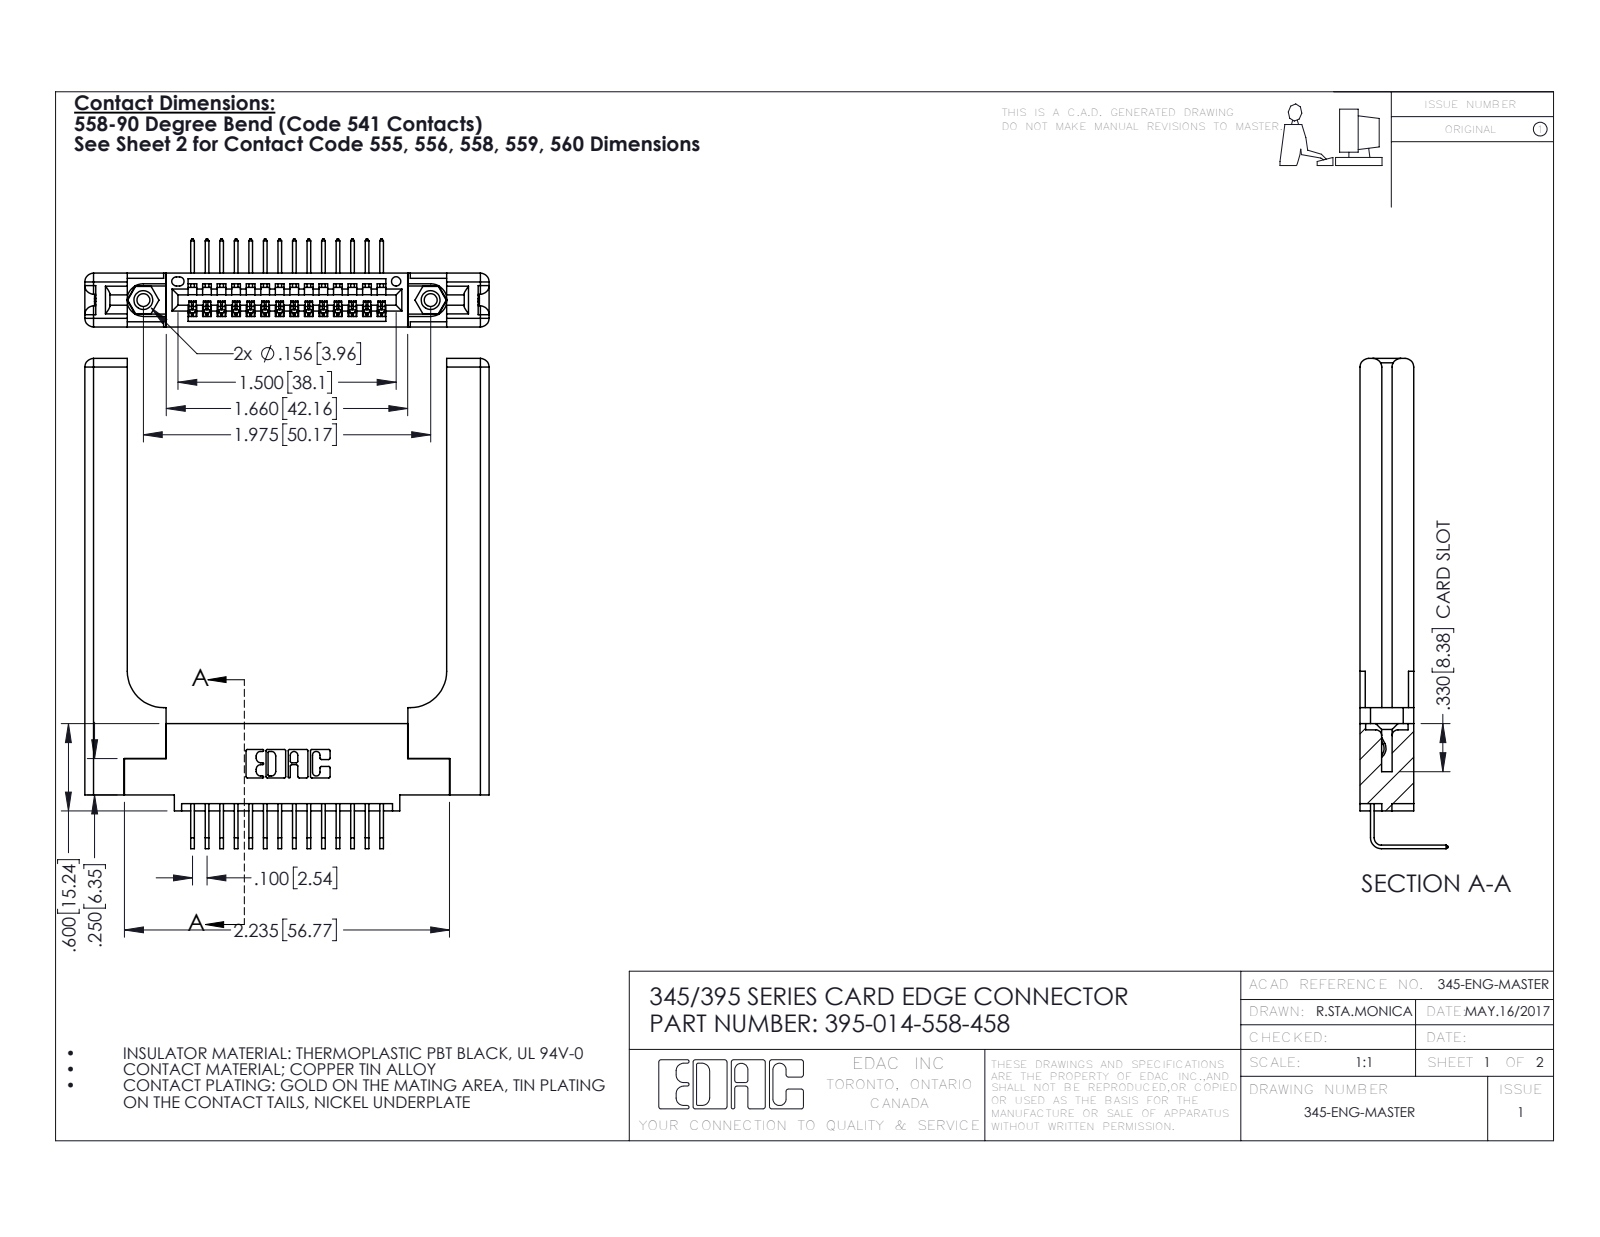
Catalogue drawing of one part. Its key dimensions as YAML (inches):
part_name: "345-292-001_558 Tail - 2; 345 Part_0.110 Offset - 0.156 Dia-TH; 395-014-558-458; 345-220-058_345-220-058 (+1 more)"
step_written_by: "SolidWorks 2016 (CONFIG_CONTROL_DESIGN)"
units: inches
bodies: {solids: 19, faces: 1226, planar: 820, cylindrical: 346, other: 60}
overall_size: [3.369, 2.779, 0.605]
volume: 0.913
surface_area: 21.47
round_holes:
  - {diameter: 0.089, count: 2}
  - {diameter: 0.125, count: 2}
  - {diameter: 0.156, count: 2}
  - {diameter: 0.064, count: 1}
round_bosses_or_shafts:
  - {diameter: 0.155, count: 2}
partial_cylinders:
  - {radius: 0.006, count: 28}
  - {radius: 0.01, count: 22}
  - {radius: 0.06, count: 16}
  - {radius: 0.007, count: 6}
  - {radius: 0.031, count: 6}
  - {radius: 0.026, count: 3}
  - {radius: 0.03, count: 2}
  - {radius: 0.031, count: 2}
face_to_face_distances: [0.37, 0.072, 0.298, 0.15, 0.148, 0.077, 0.22, 0.2, 2.196, 0.098]
hole_center_spacings: [0.27, 1.742, 1.975]
